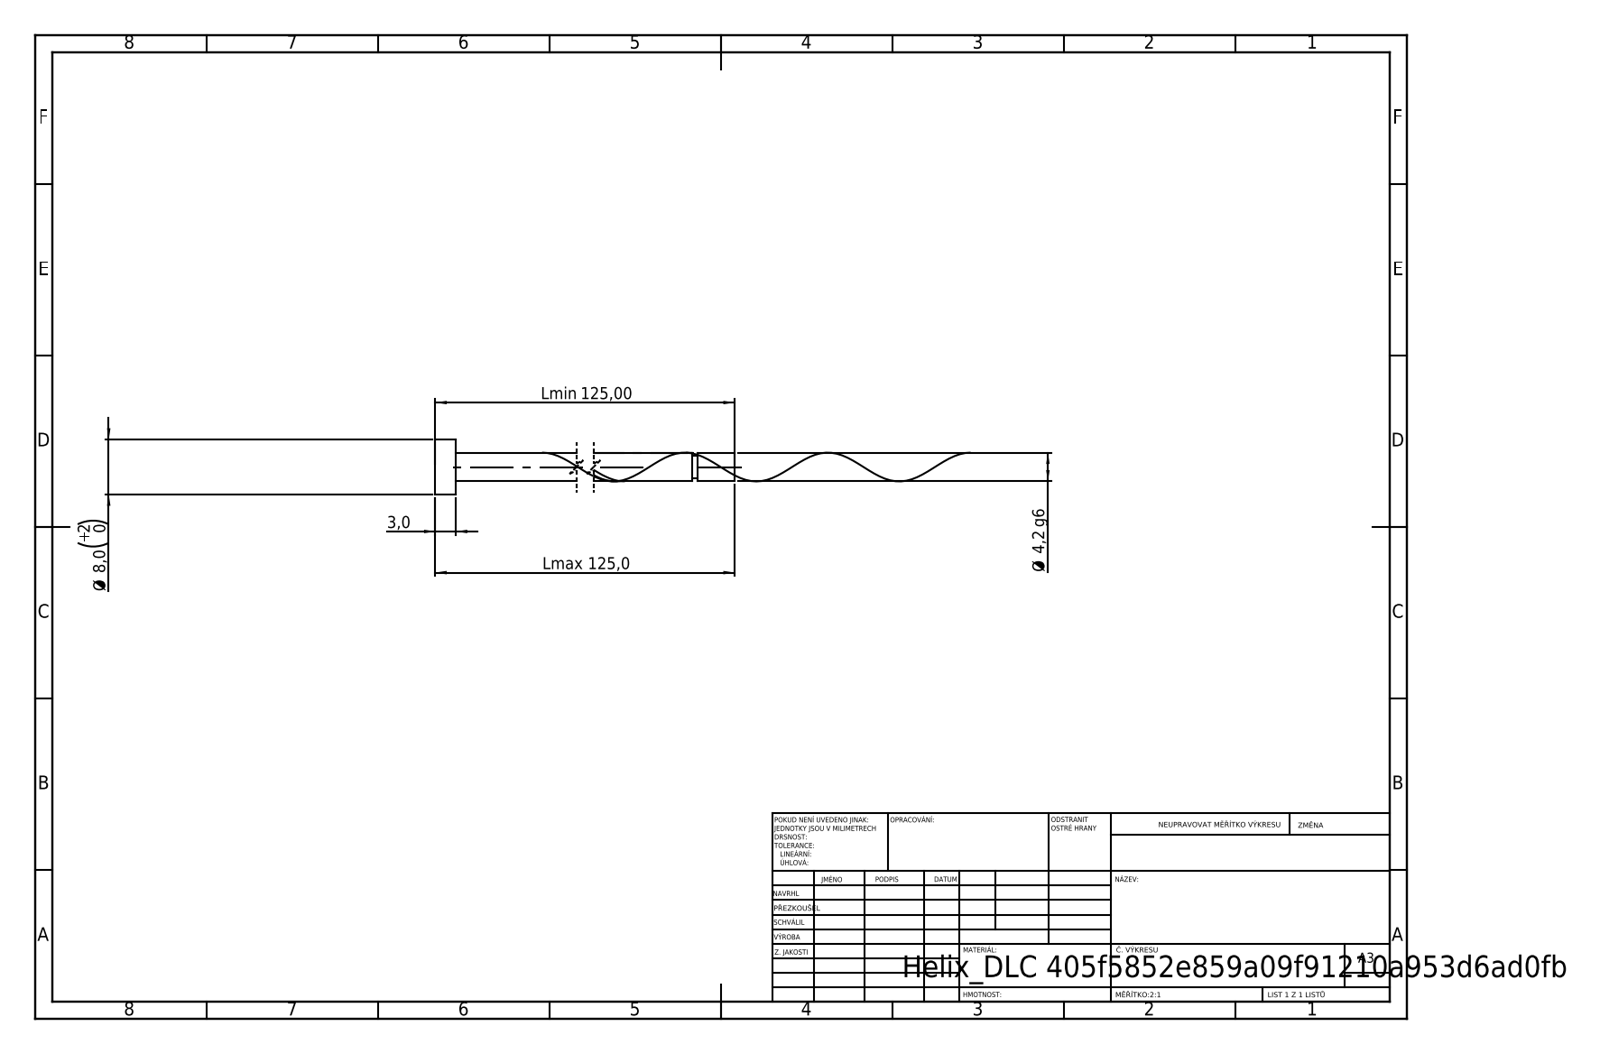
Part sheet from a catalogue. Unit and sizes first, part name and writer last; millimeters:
Units: millimetres
Overall size (bounding box): 125 × 8 × 8
Round bosses / shafts (diameter × count): ⌀8 ×1, ⌀4.2 ×1, ⌀3.36 ×1
Main face-to-face distances: 3, 125, 122, 119.57, 116.57, 5.43, 118.73, 115.73, 0.84, 6.27
Volume: 1 820 mm³ · Surface area: 1 825 mm²
Bodies: 1 solid, 21 faces (6 planar, 14 cylindrical, 1 other)
STEP written by: SolidWorks 2019 (CONFIG_CONTROL_DESIGN)
